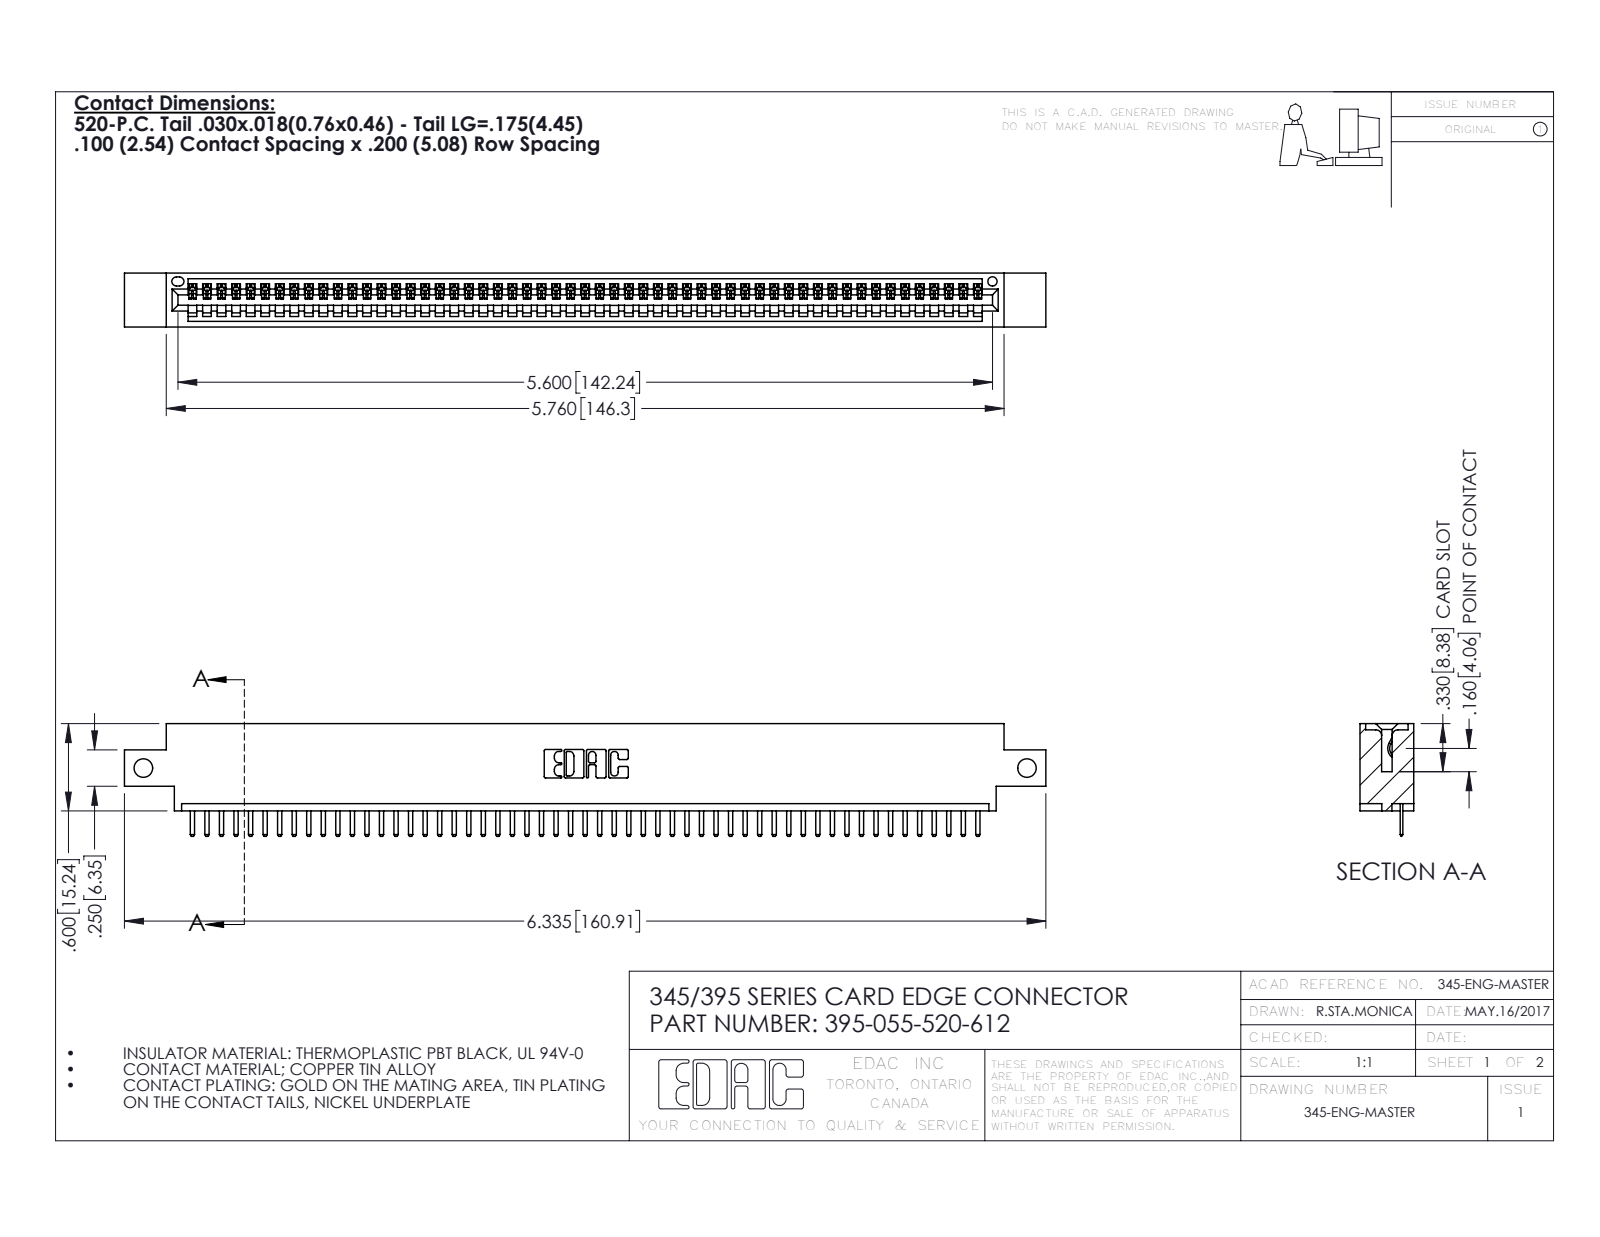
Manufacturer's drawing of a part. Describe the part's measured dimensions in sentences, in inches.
The part is named "345 Part_0.170 Offset - Side Mount; 345-292-001_345-293-120; 395-055-520-612". Its 3-D file was written by "SolidWorks 2016 (CONFIG_CONTROL_DESIGN)". It is 56 solids with 3540 faces: 2394 planar, 1146 cylindrical and 0 other. Overall it measures 6.335 by 0.775 by 0.37 inches. Its volume is 0.917 cubic inches and its surface area 30.41 square inches. Round holes: 2 of diameter 0.128, 1 of diameter 0.064. Partial cylindrical surfaces (rounded edges, fillets, slot ends): 112 of radius 0.01, 110 of radius 0.006, 22 of radius 0.01, 6 of radius 0.007, 6 of radius 0.031, 3 of radius 0.026, 2 of radius 0.031, 2 of radius 0.04. The main face-to-face distances are 0.298, 0.072, 0.37, 0.2, 0.098, 0.272, 0.025, 0.225, 0.072, 0.175. The hole center spacings are 6.075.
